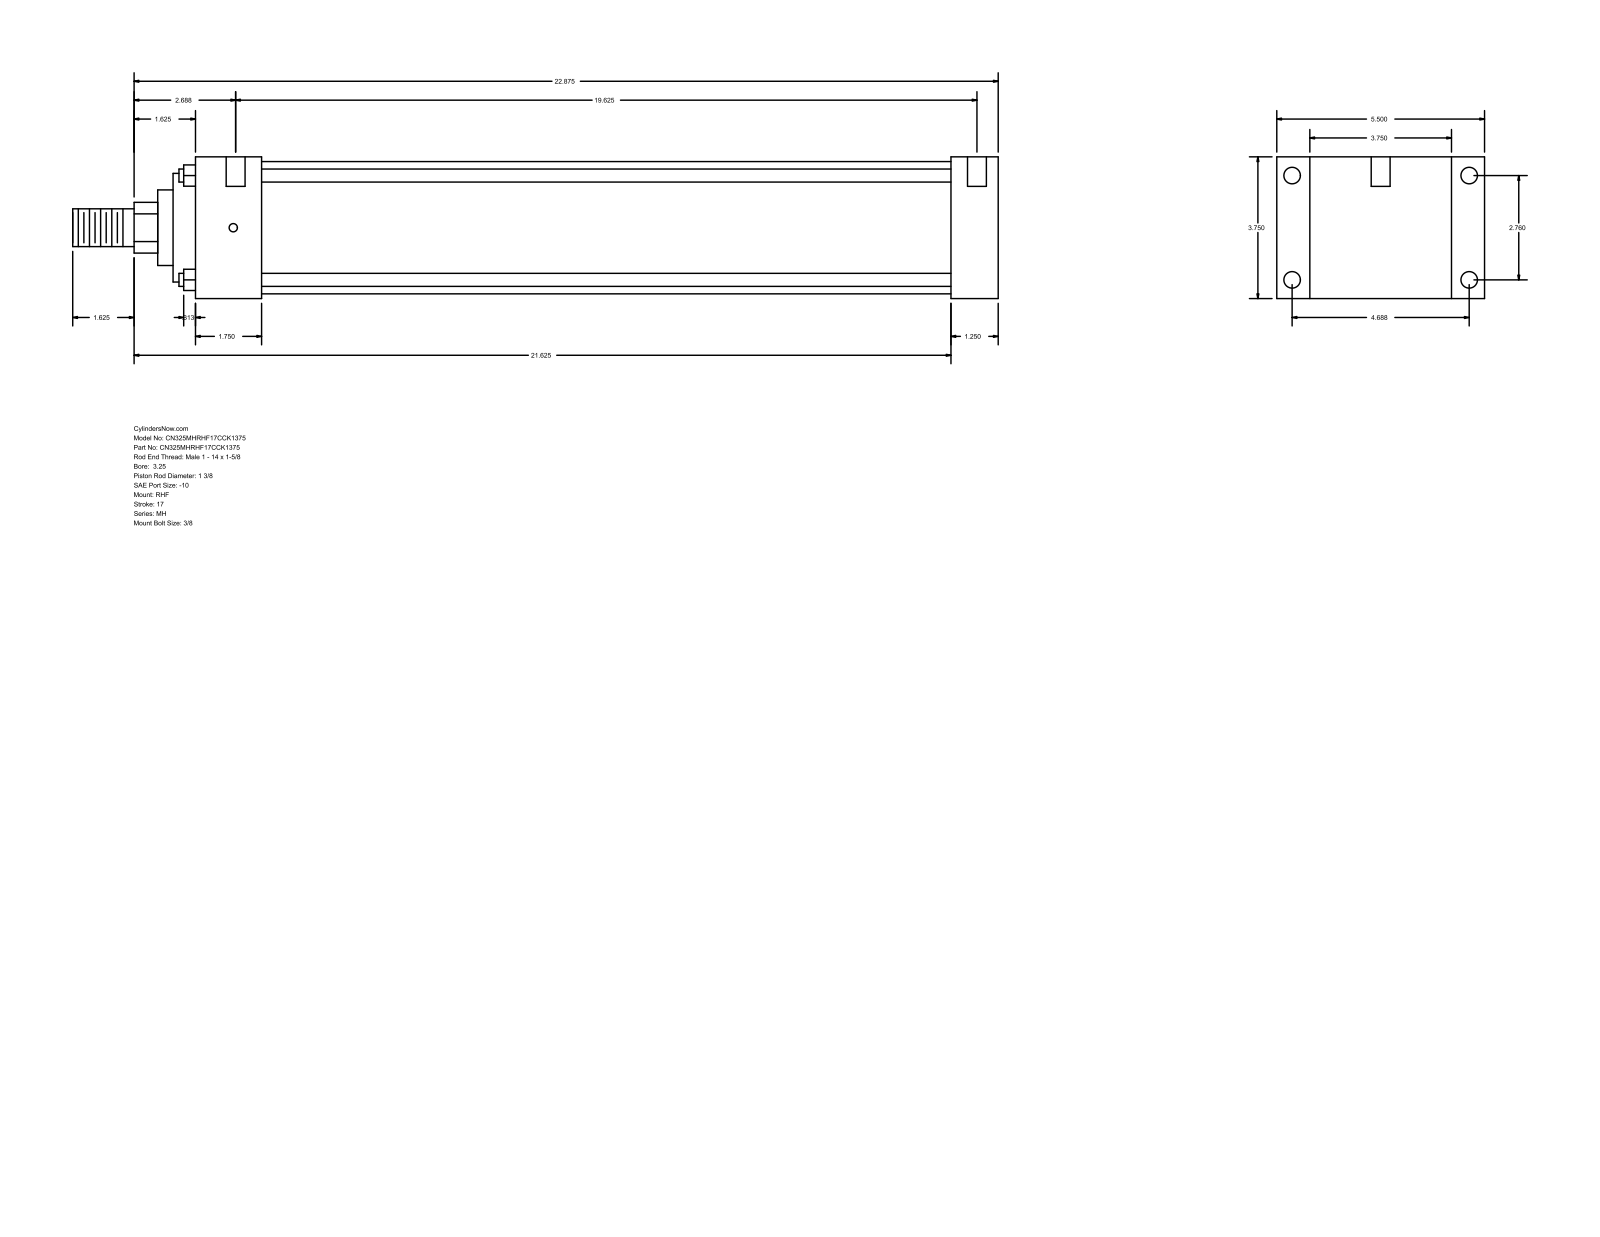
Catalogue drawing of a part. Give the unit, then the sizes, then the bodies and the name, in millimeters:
Units: millimetres
Overall size (bounding box): 622.3 × 139.7 × 95.25
Round holes (diameter × count): ⌀5.56 ×4, ⌀11.13 ×4, ⌀12.7 ×2
Round bosses / shafts (diameter × count): ⌀8.76 ×4, ⌀88.9 ×1, ⌀73.03 ×1, ⌀50.8 ×1, ⌀34.92 ×1, ⌀25.4 ×1
Partial cylindrical surfaces — rounded edges, fillets, slot ends (radius × count): R17.06 ×1
Main face-to-face distances: 95.24, 31.75, 22.23, 117.47, 508, 539.75, 139.7, 44.45, 463.55, 495.3
Hole centre spacings: 70.1, 119.06, 138.16, 504.83, 1.59, 4.76, 498.48, 500.07
Bodies: 0 solids, 90 faces (61 planar, 29 cylindrical, 0 other)
Part name (STEP PRODUCT): MH_RHF__0325_1.375
STEP written by: GSSL Pune (CONFIG_CONTROL_DESIGN)
